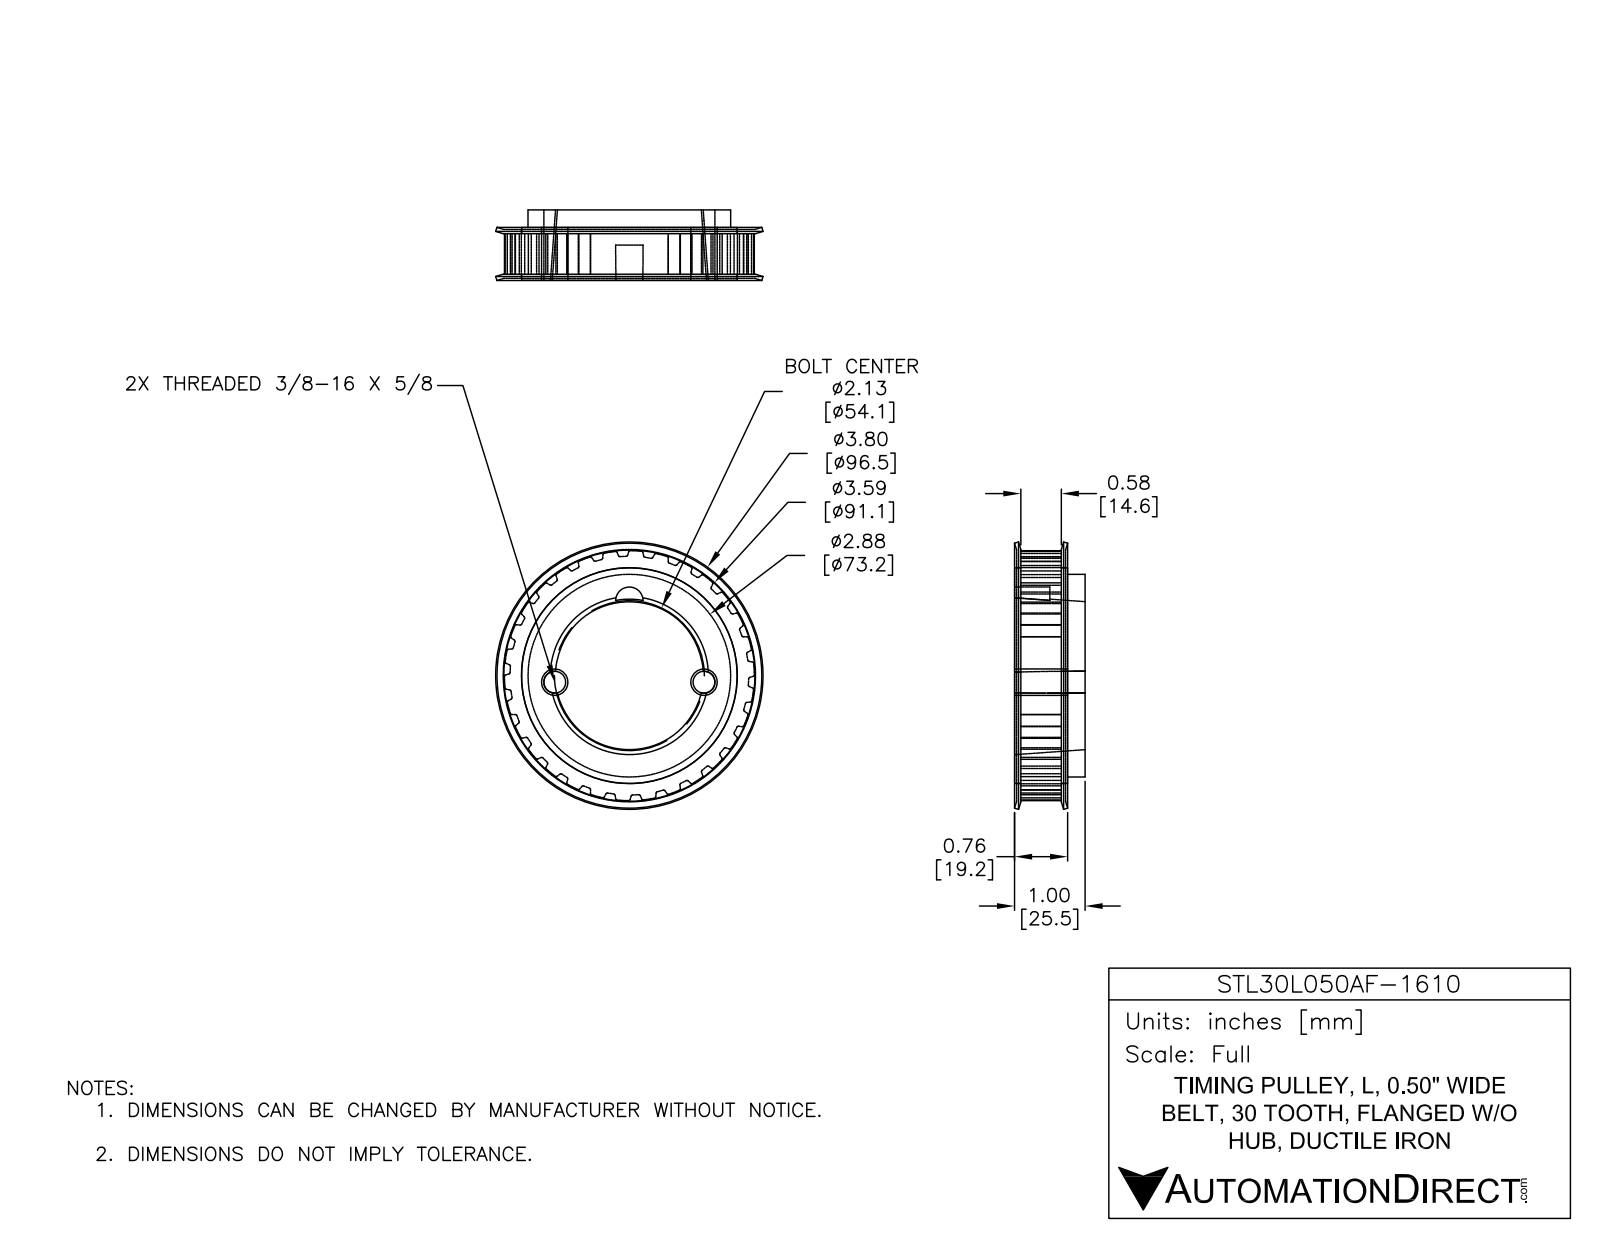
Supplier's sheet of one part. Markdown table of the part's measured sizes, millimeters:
| quantity | value |
| --- | --- |
| part name | STL30L050AF-1610 |
| STEP written by | SolidWorks 2018 (AUTOMOTIVE_DESIGN) |
| units | millimeters |
| bodies | 1 solid, 303 faces (100 planar, 189 cylindrical, 14 other) |
| overall size | 96.52 × 96.52 × 25.46 |
| volume | 83 168 mm³ |
| surface area | 26 034 mm² |
| round holes (diameter × count) | 77.9 × 1 |
| round bosses / shafts (diameter × count) | 77.79 × 1, 73.15 × 1 |
| partial cylindrical surfaces (radius × count) | 0.38 × 60, 0.51 × 60, 3.94 × 2, 4.95 × 1, 45.1 × 1 |
| main face-to-face distances | 25.4, 7.04, 24.7, 17.66, 18.36, 0.7, 1.53, 16.13, 6.35, 0.69 |
